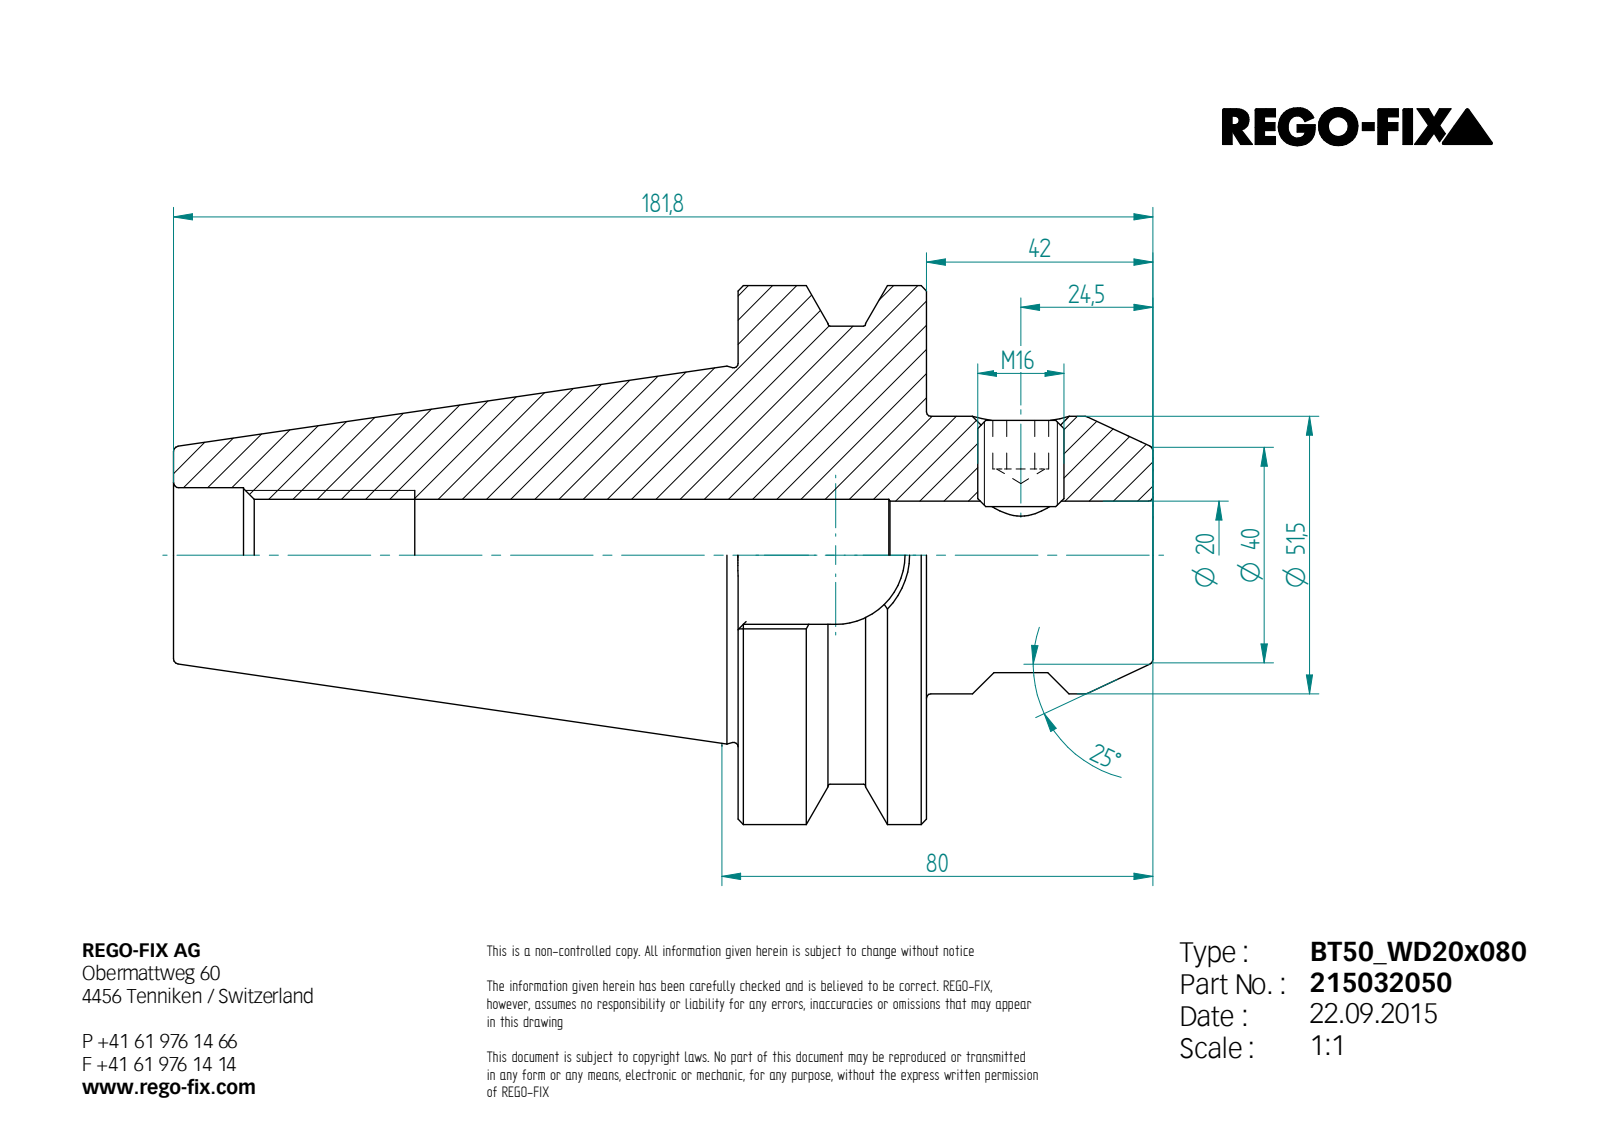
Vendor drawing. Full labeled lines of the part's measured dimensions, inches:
STEP written by: Unknown (AUTOMOTIVE_DESIGN)
Units: inches
Bodies: 2 solids, 94 faces (45 planar, 18 cylindrical, 31 other)
Overall size (bounding box): 7.157 × 3.937 × 3.937
Volume: 31.26 in³ · Surface area: 98.34 in²
Round holes (diameter × count): ⌀0.545 ×1, ⌀0.787 ×1, ⌀0.817 ×1, ⌀0.984 ×1
Round bosses / shafts (diameter × count): ⌀3.937 ×1, ⌀3.346 ×1, ⌀2.028 ×1, ⌀0.63 ×1
Partial cylindrical surfaces — rounded edges, fillets, slot ends (radius × count): R0.02 ×4, R0.506 ×1
Main face-to-face distances: 1.378, 3.031, 1.654, 2.783, 4.126, 5.504, 7.157, 1.012, 0.352, 1.364
